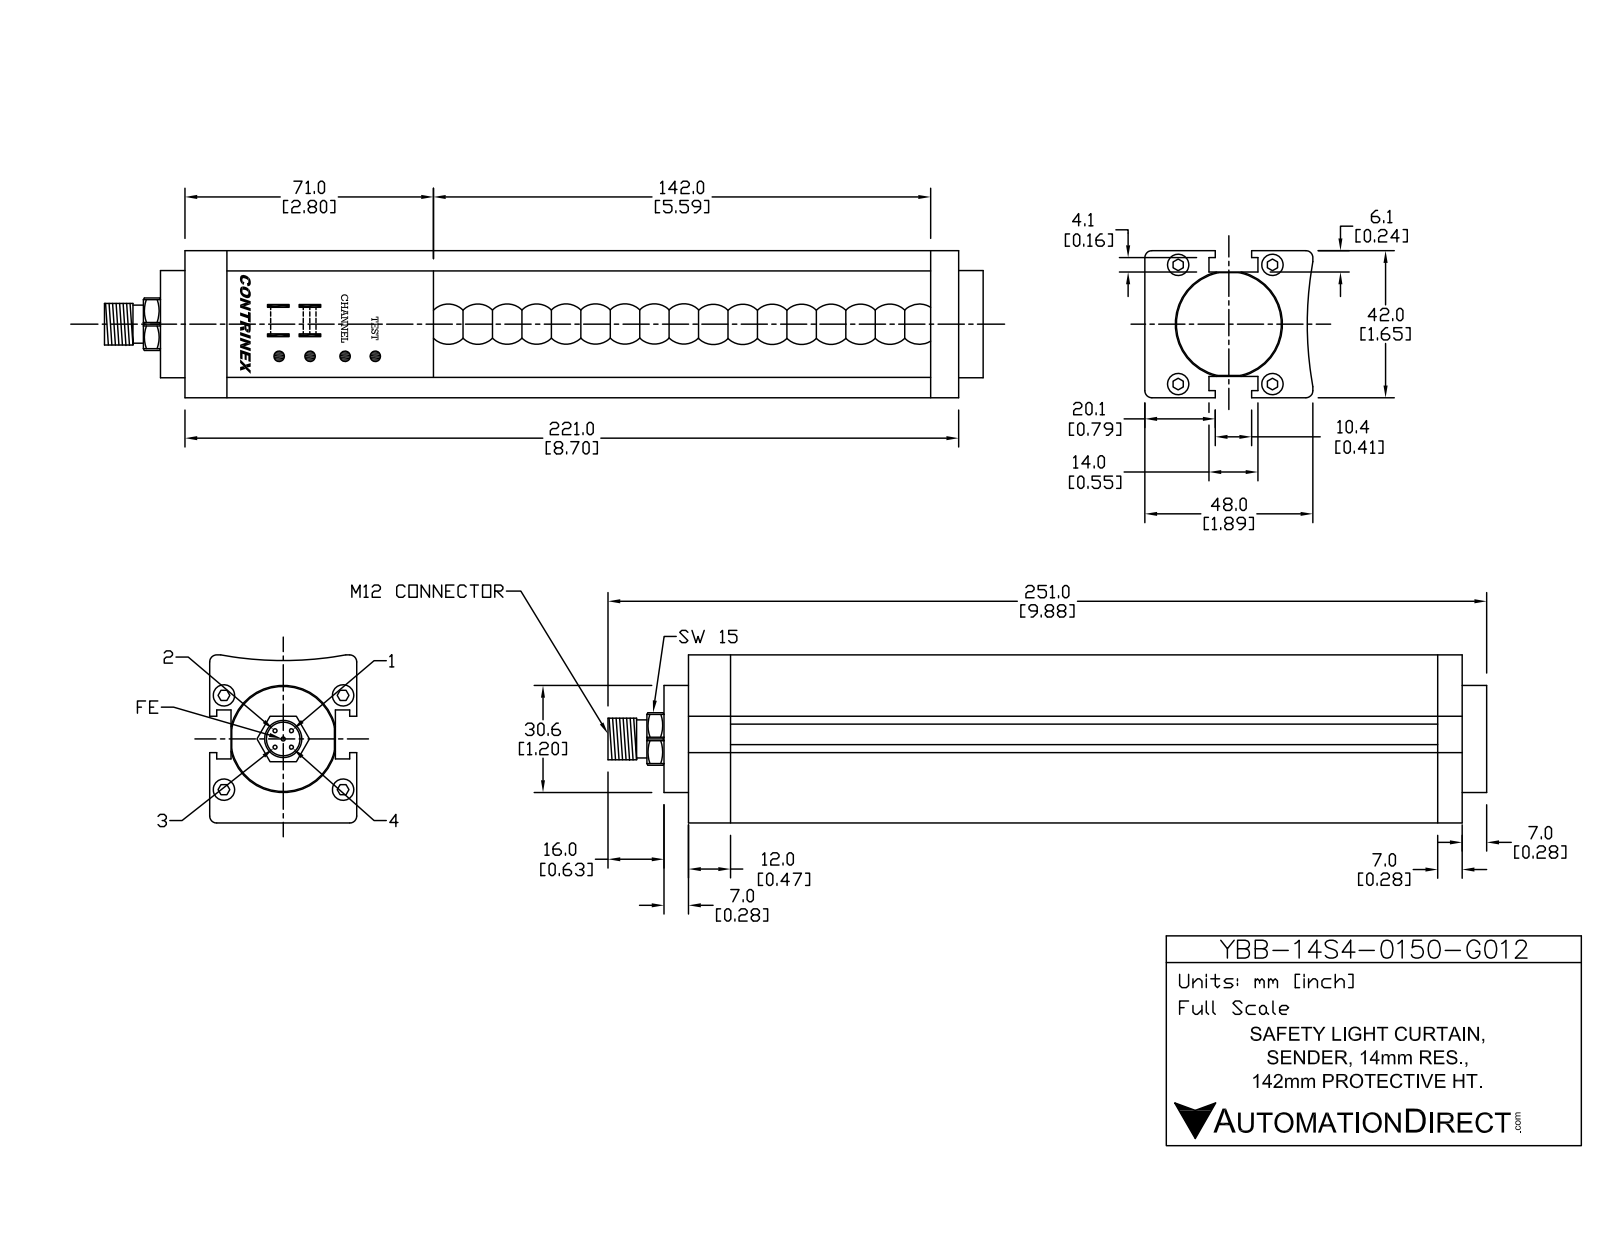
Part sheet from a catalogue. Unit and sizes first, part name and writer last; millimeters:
Units: millimetres
Overall size (bounding box): 251 × 48 × 42
Round holes (diameter × count): ⌀6 ×4, ⌀8.5 ×1, ⌀32 ×1
Round bosses / shafts (diameter × count): ⌀1 ×5, ⌀5.5 ×4, ⌀30.6 ×1, ⌀12 ×1, ⌀10.5 ×1
Partial cylindrical surfaces — rounded edges, fillets, slot ends (radius × count): R1 ×48, R0.5 ×4, R0.55 ×2, R8.2 ×1, R100 ×1
Main face-to-face distances: 6.3, 35.7, 42, 201, 29.4, 8, 12, 213, 221, 209
Hole centre spacings: 21.04, 22.34, 26.9, 34, 43.35
Volume: 406 321 mm³ · Surface area: 64 999 mm²
Bodies: 19 solids, 440 faces (208 planar, 168 cylindrical, 64 other)
Part name (STEP PRODUCT): YBB-14S4-0150-G012
STEP written by: SolidWorks 2016 (AUTOMOTIVE_DESIGN)
